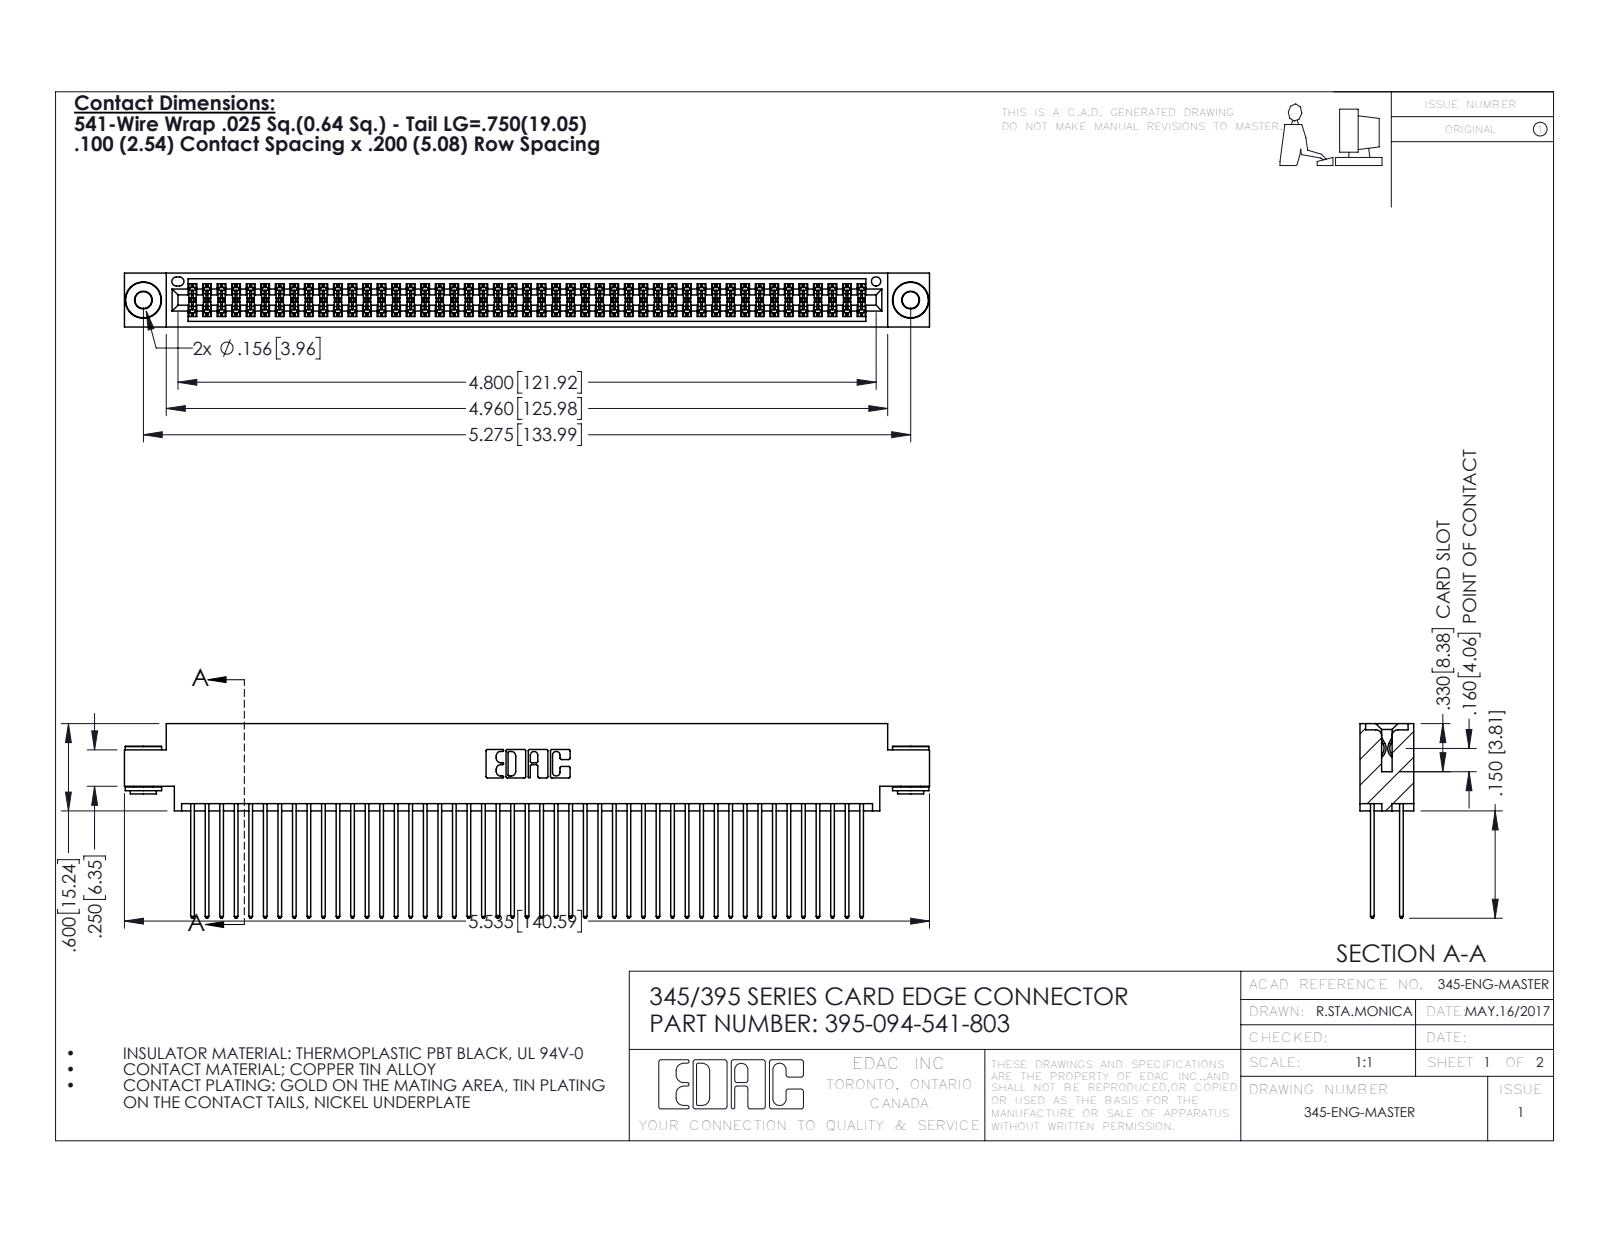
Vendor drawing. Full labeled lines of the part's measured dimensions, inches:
Part name (STEP PRODUCT): 395-094-541-803; 345-250-002_345-250-002-102; 345 Part_0.170 Offset - 0.156 Dia-TH; 345-292-001_345-293-141
STEP written by: SolidWorks 2016 (CONFIG_CONTROL_DESIGN)
Units: inches
Bodies: 97 solids, 4868 faces (3196 planar, 1664 cylindrical, 8 other)
Overall size (bounding box): 5.535 × 1.337 × 0.37
Volume: 0.863 in³ · Surface area: 37.04 in²
Round holes (diameter × count): ⌀0.116 ×2, ⌀0.156 ×2, ⌀0.064 ×1
Round bosses / shafts (diameter × count): ⌀0.25 ×2, ⌀0.18 ×2, ⌀0.136 ×2
Partial cylindrical surfaces — rounded edges, fillets, slot ends (radius × count): R0.006 ×141, R0.01 ×94, R0.01 ×22, R0.007 ×6, R0.031 ×6, R0.026 ×3, R0.014 ×2, R0.019 ×2
Main face-to-face distances: 0.072, 0.298, 0.2, 0.098, 0.272, 0.025, 0.37, 0.225, 0.175, 0.149
Hole centre spacings: 0.27, 5.039, 5.275
